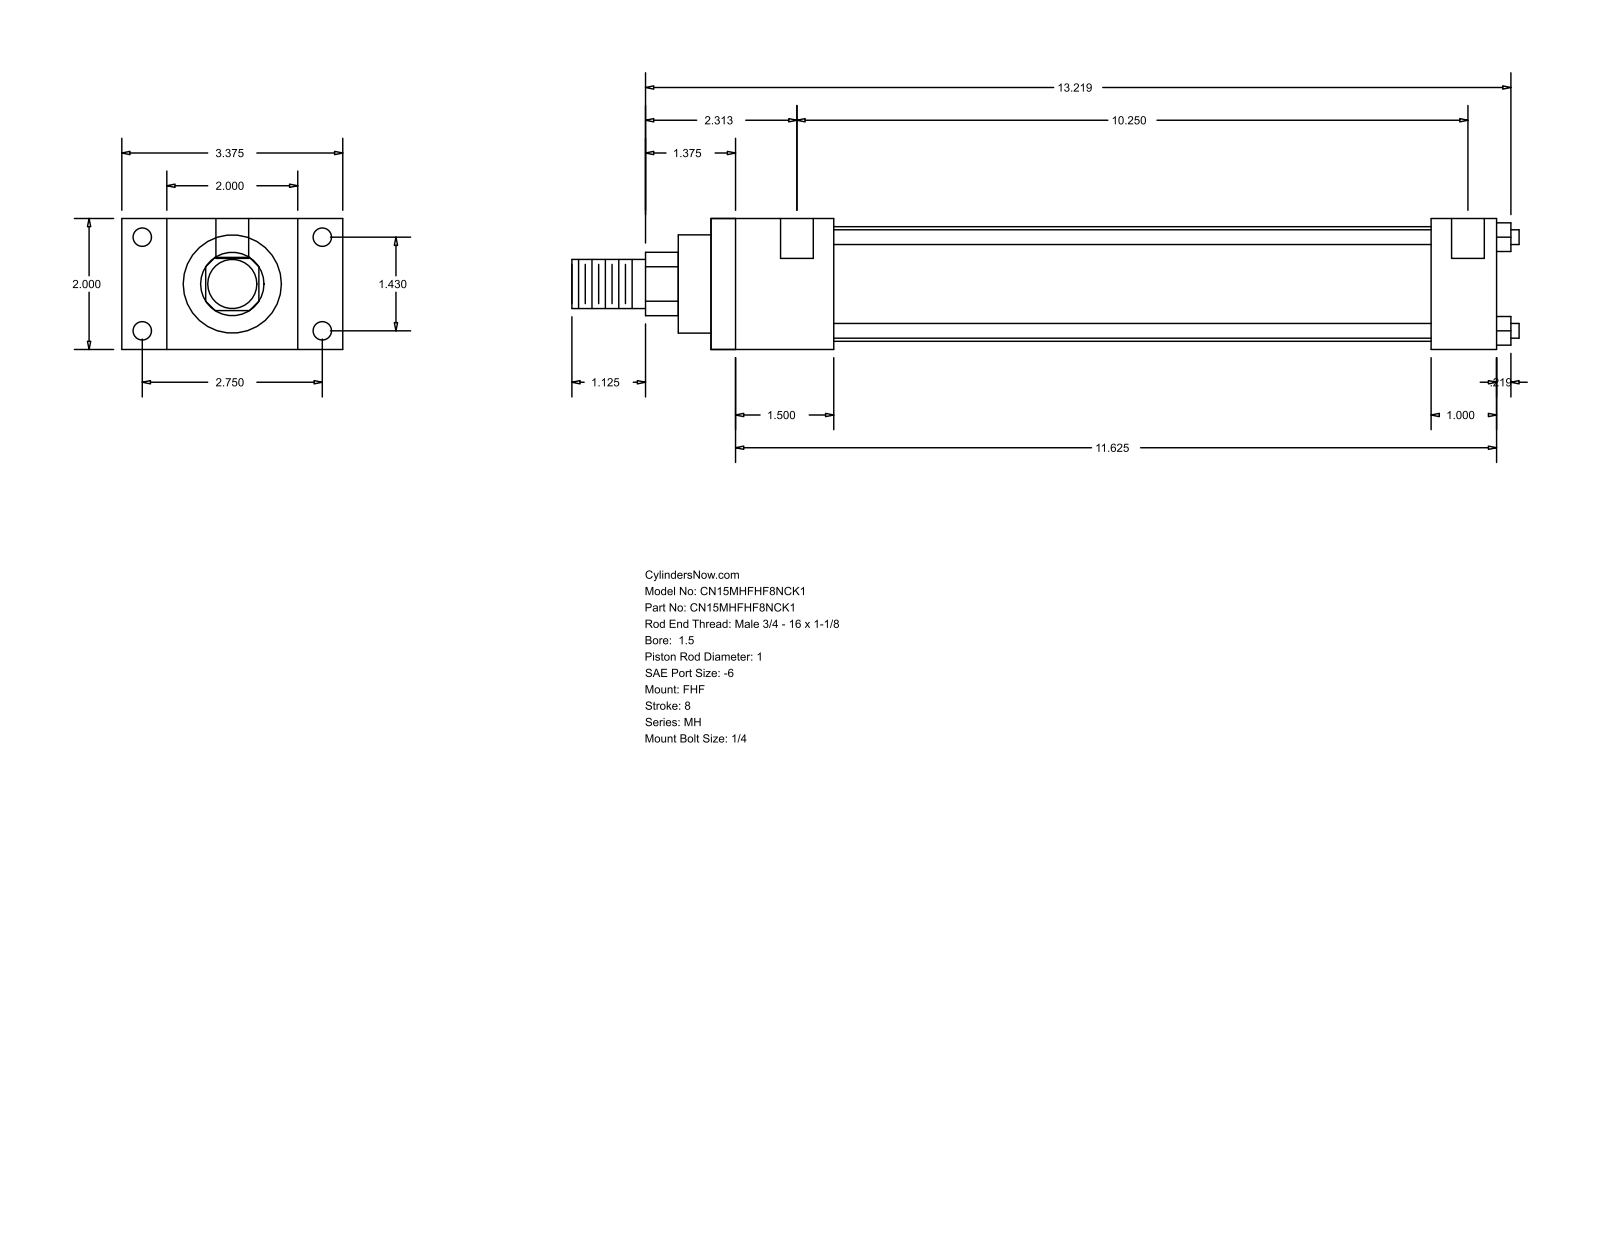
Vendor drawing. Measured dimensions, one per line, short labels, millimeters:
name: MH_FHF__0150_1
written by: GSSL Pune (CONFIG_CONTROL_DESIGN)
unit: mm
bodies: 0 solids, 88 faces (60 planar, 28 cylindrical, 0 other)
size: 367.51 × 85.72 × 50.8
holes: 4× ⌀5.56, 4× ⌀7.14, 2× ⌀12.7
bosses: 4× ⌀5.71, 1× ⌀44.45, 1× ⌀38.1, 1× ⌀25.4, 1× ⌀19.05
rounds: 1× R12.29
face distances: 50.8, 17.46, 68.26, 47.63, 85.72, 304.8, 257.17, 25.4, 279.4, 231.77
hole spacings: 36.32, 69.84, 78.72, 263.53, 3.18, 260.35
